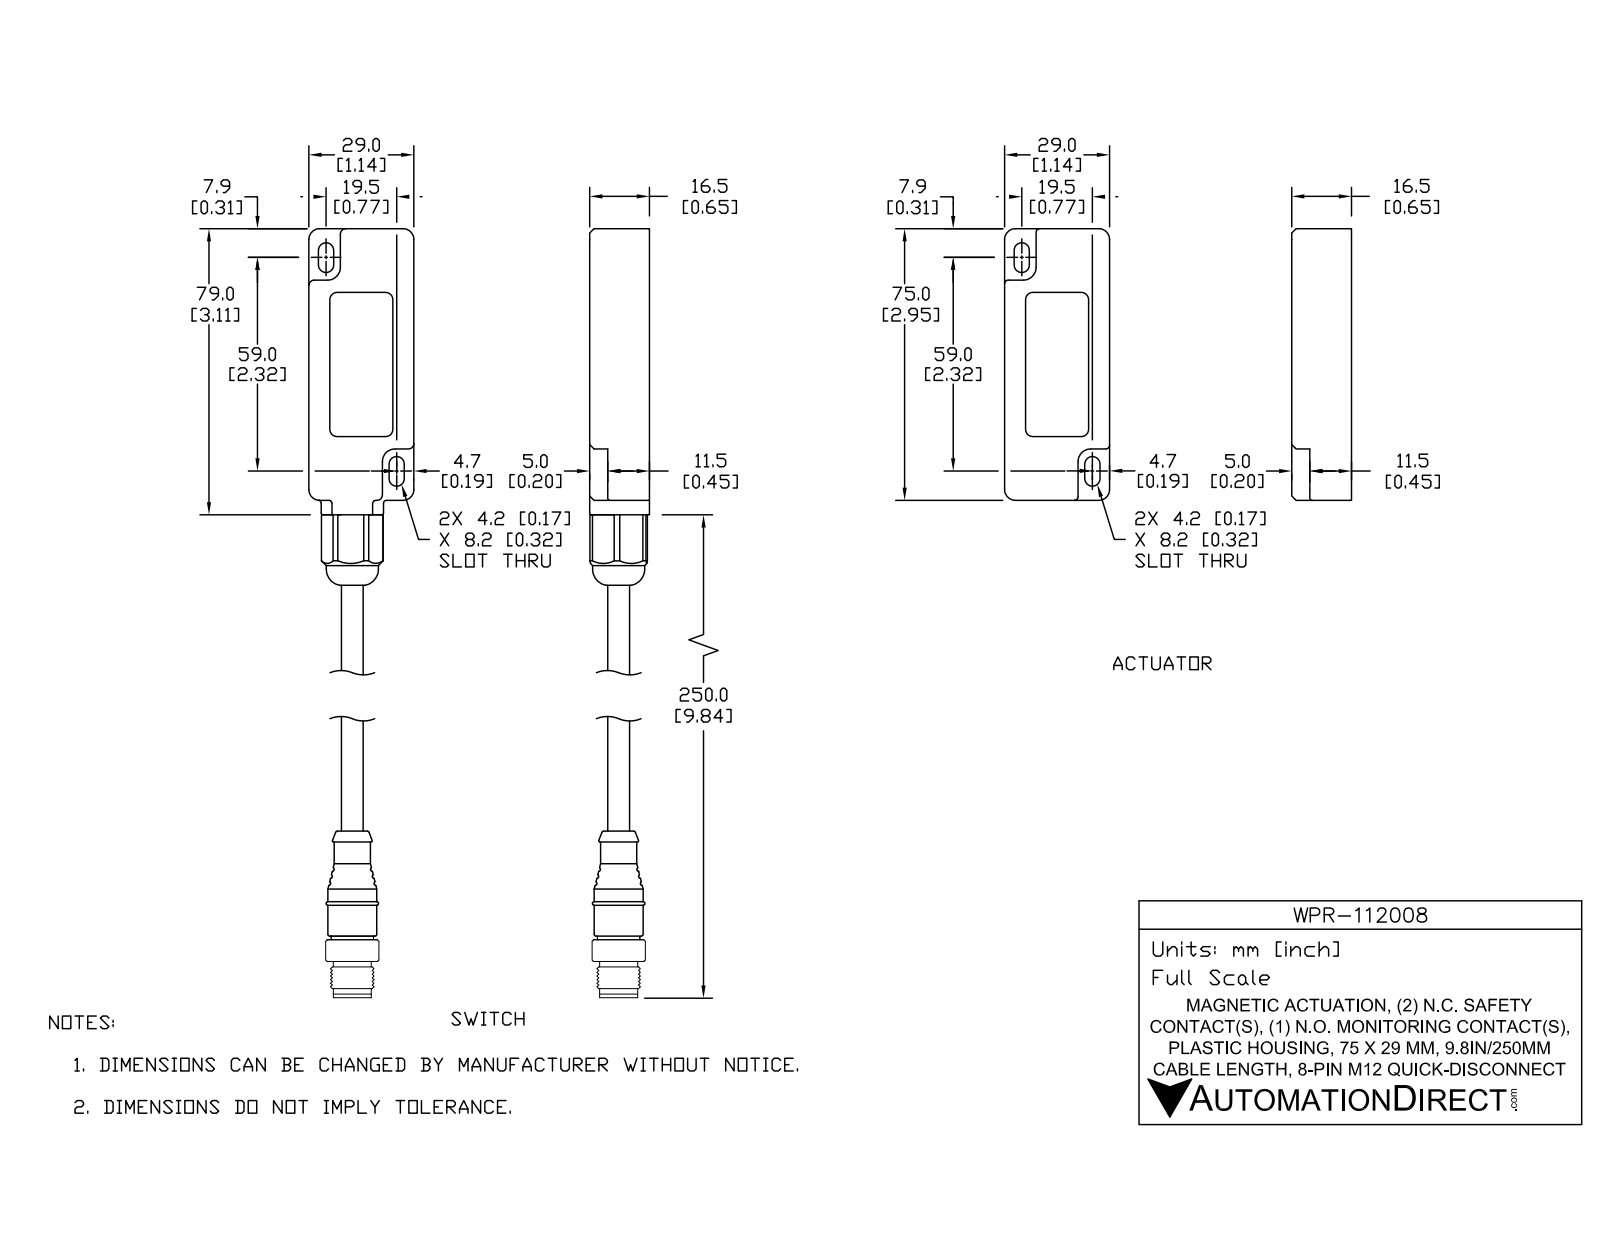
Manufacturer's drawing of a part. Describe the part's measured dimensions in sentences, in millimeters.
The part is named "WPR-112008_2; WPR-112008_1; WPR-112008". Its 3-D file was written by "SolidWorks 2017 (AUTOMOTIVE_DESIGN)". It is 11 solids with 1294 faces: 573 planar, 348 cylindrical and 373 other. Overall it measures 329 by 59 by 16.5 millimeters. Its volume is 43 100 cubic millimeters and its surface area 42 180 square millimeters. Round holes: 4 of diameter 5, 1 of diameter 7, 1 of diameter 8.3, 1 of diameter 11.8, 1 of diameter 12. Round bosses or shafts: 8 of diameter 0.8, 4 of diameter 4.9, 4 of diameter 2, 2 of diameter 2.3, 1 of diameter 14.4, 1 of diameter 13.5, 1 of diameter 11.9, 1 of diameter 11.7. Partial cylindrical surfaces (rounded edges, fillets, slot ends): 85 of radius 0.5, 20 of radius 1, 10 of radius 0.2, 8 of radius 1.2, 8 of radius 2, 8 of radius 2.1, 8 of radius 3, 4 of radius 0.6. The main face-to-face distances are 1.8, 14.6, 30, 27.2, 16.4, 1.7, 14.5, 1.9, 12.8, 14.7. The hole center spacings are 52, 22.9, 37.1, 59.5, 59.6.
